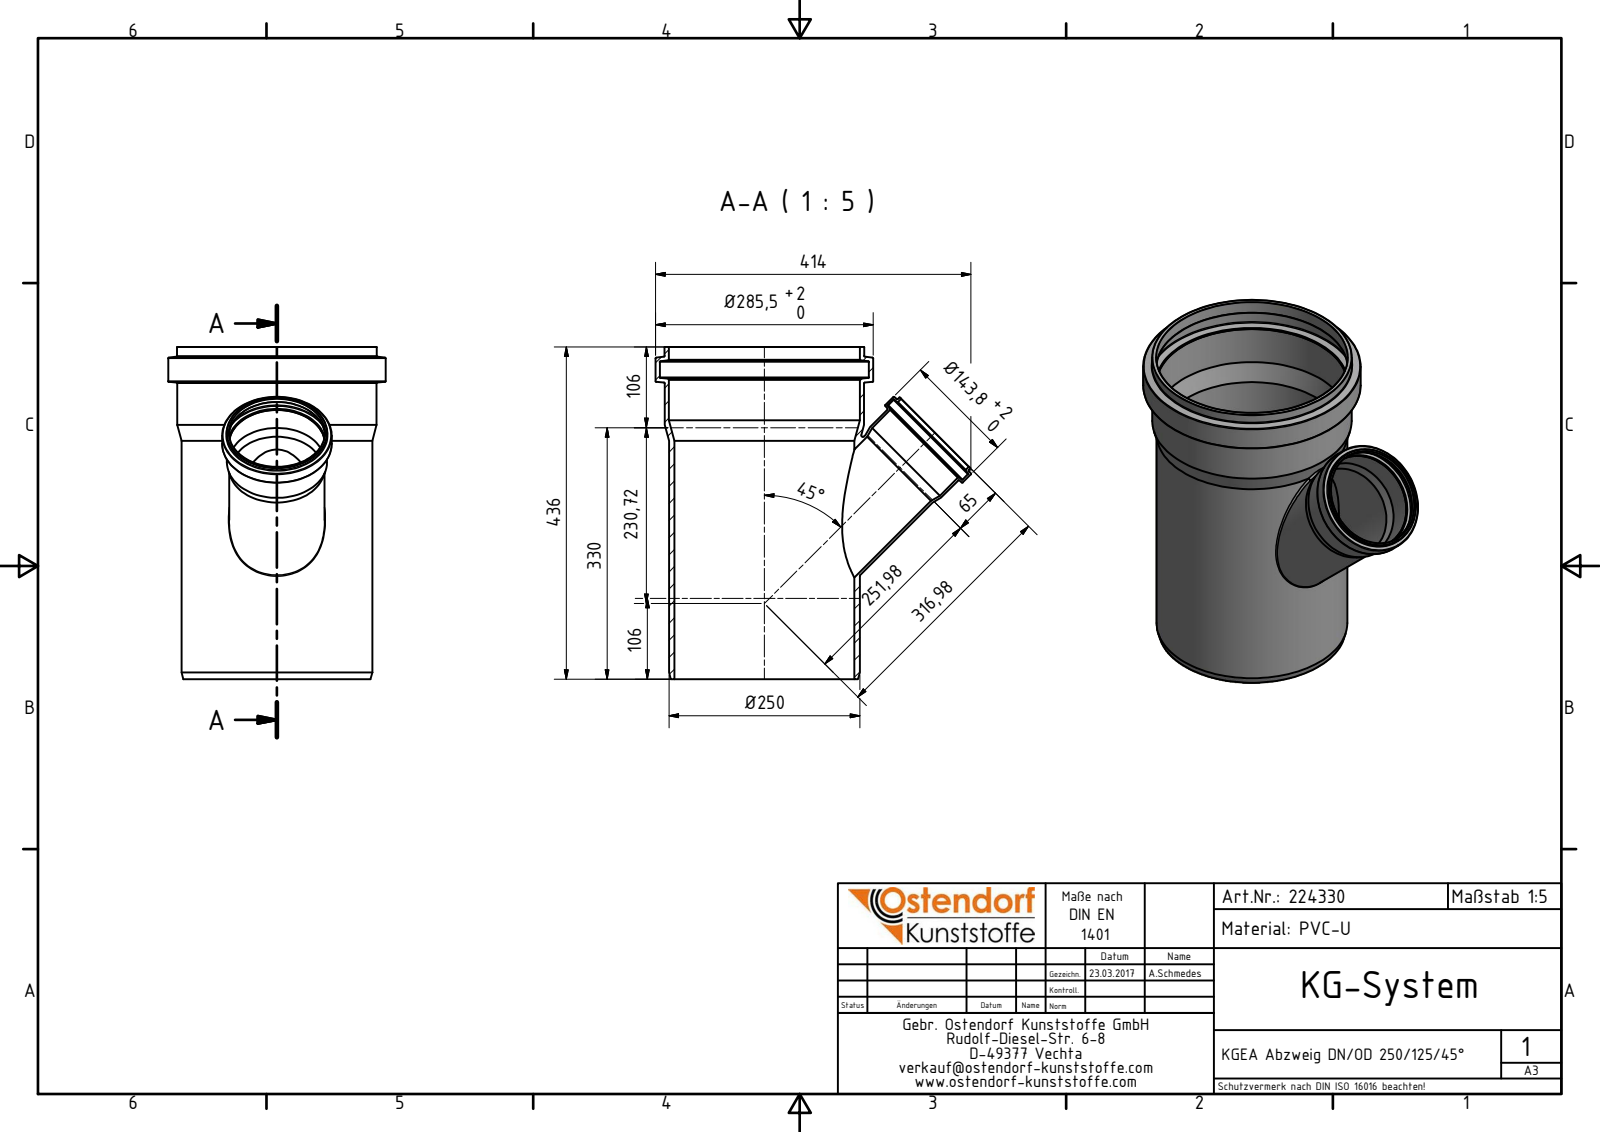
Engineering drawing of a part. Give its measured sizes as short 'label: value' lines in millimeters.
name: 224330 KGEA Abzweig DN_OD 250_125_45°
written by: Autodesk Inventor 2016 (AUTOMOTIVE_DESIGN)
unit: mm
bodies: 1 solid, 58 faces (5 planar, 18 cylindrical, 35 other)
size: 436 × 414 × 285.5
volume: 2 455 000 mm³; area: 820 614 mm²
holes: 2× ⌀126, 1× ⌀118.8, 1× ⌀125.7, 1× ⌀138, 1× ⌀236.3, 1× ⌀250.8, 1× ⌀251.1, 1× ⌀274.5
bosses: 1× ⌀285.5, 1× ⌀262.1, 1× ⌀261.8, 1× ⌀250.5, 1× ⌀143.8, 1× ⌀131.8, 1× ⌀131.5, 1× ⌀125.2
face distances: 436, 392.77, 43.23, 20.67
